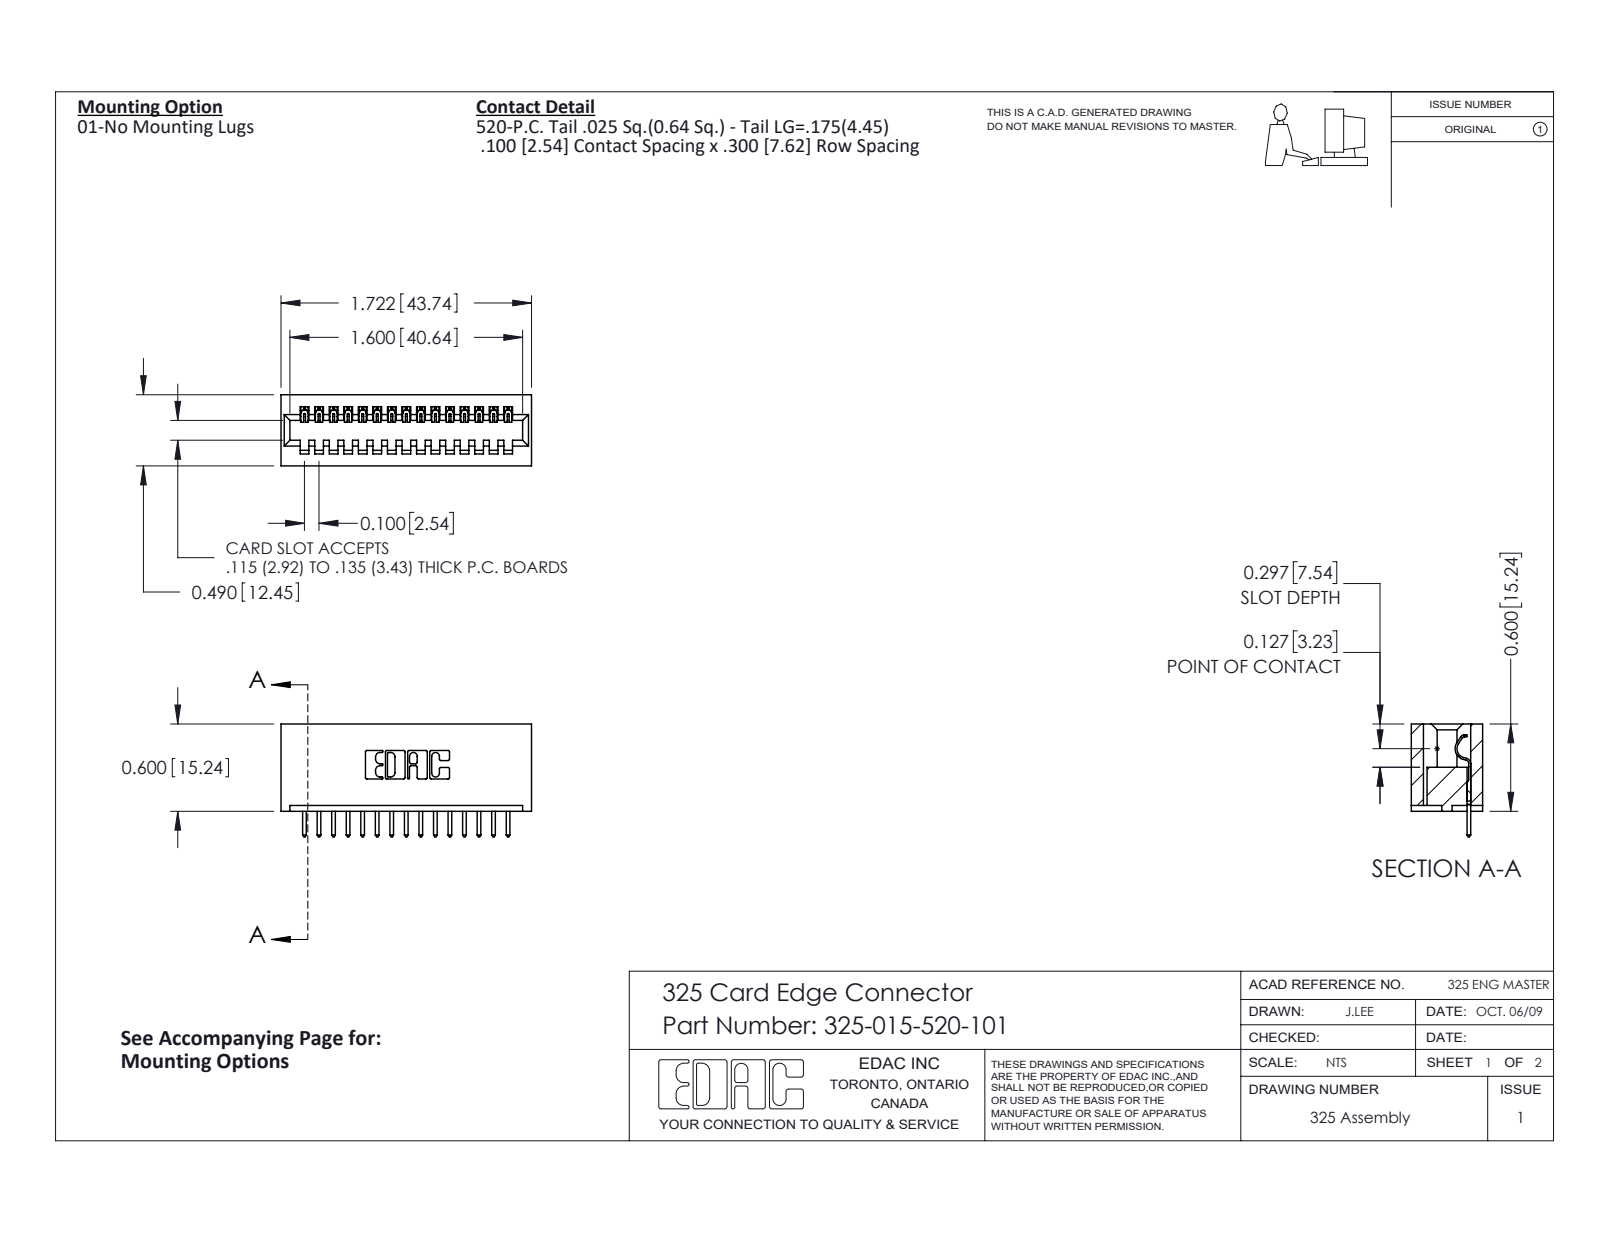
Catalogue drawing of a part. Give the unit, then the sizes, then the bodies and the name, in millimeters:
Units: millimetres
Overall size (bounding box): 43.7 × 19.7 × 12.4
Partial cylindrical surfaces — rounded edges, fillets, slot ends (radius × count): R0.2 ×30, R0.3 ×30, R0.3 ×22, R0.2 ×6, R0.8 ×6, R0.7 ×3, R0.4 ×1, R0.6 ×1
Main face-to-face distances: 7.6, 2.1, 10.3, 12.4, 2.5, 5.1, 10.2, 2.7, 9.7, 0.6
Volume: 5 870 mm³ · Surface area: 6 291 mm²
Bodies: 16 solids, 976 faces (696 planar, 280 cylindrical, 0 other)
Part name (STEP PRODUCT): 325-292-001_325-293-120; 325-015-520-101; 325 Part_Lugless
STEP written by: SolidWorks 2016 (CONFIG_CONTROL_DESIGN)
